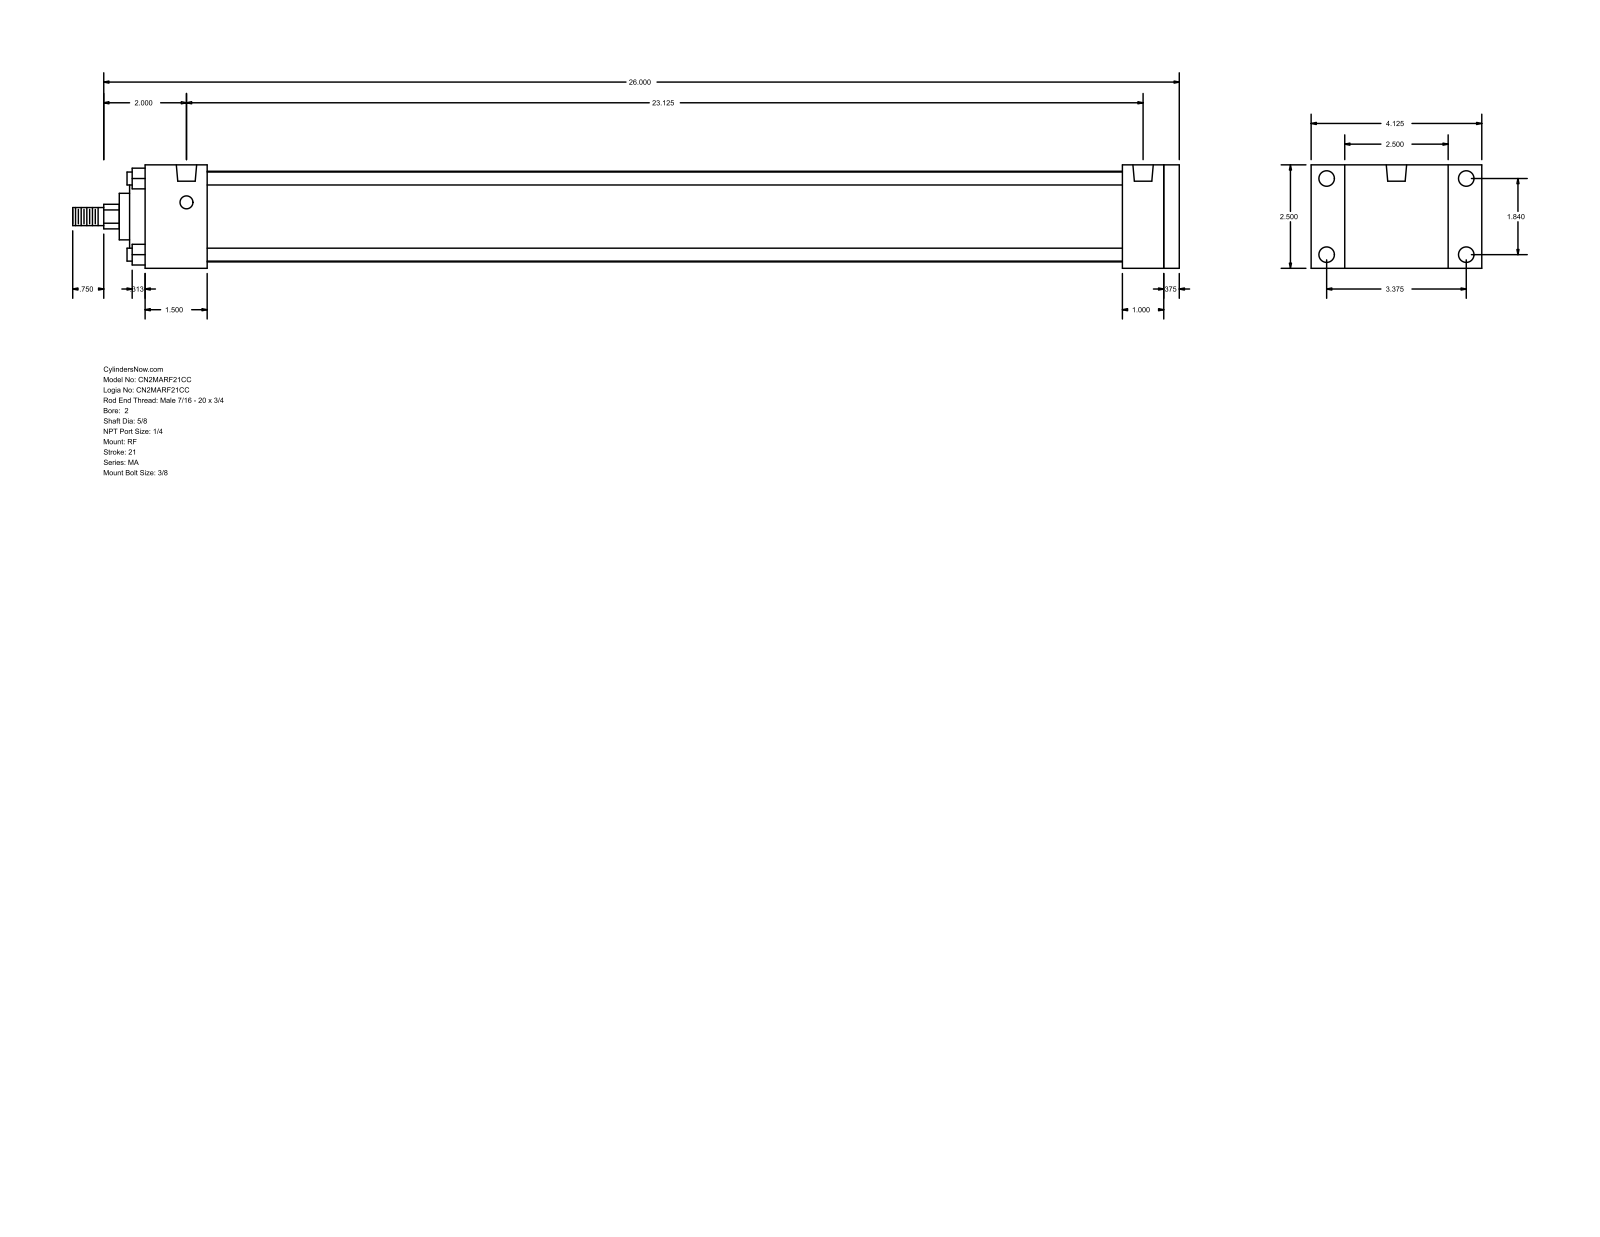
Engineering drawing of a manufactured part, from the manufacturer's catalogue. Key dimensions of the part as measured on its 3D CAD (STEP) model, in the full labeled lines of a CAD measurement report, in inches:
Part name (STEP PRODUCT): MA_RF__0200_0.625
STEP written by: GSSL Pune (CONFIG_CONTROL_DESIGN)
Units: inches
Bodies: 0 solids, 94 faces (65 planar, 29 cylindrical, 0 other)
Overall size (bounding box): 26.75 × 4.125 × 2.5
Round holes (diameter × count): ⌀0.313 ×4, ⌀0.375 ×4, ⌀0.492 ×2
Round bosses / shafts (diameter × count): ⌀0.313 ×4, ⌀2.19 ×1, ⌀2 ×1, ⌀1.125 ×1, ⌀0.625 ×1, ⌀0.437 ×1
Partial cylindrical surfaces — rounded edges, fillets, slot ends (radius × count): R0.297 ×1
Main face-to-face distances: 2.5, 0.375, 25, 1, 1.5, 24.625, 23.125, 23.5, 23.625, 22.125
Hole centre spacings: 1.84, 3.375, 3.844, 23.125
